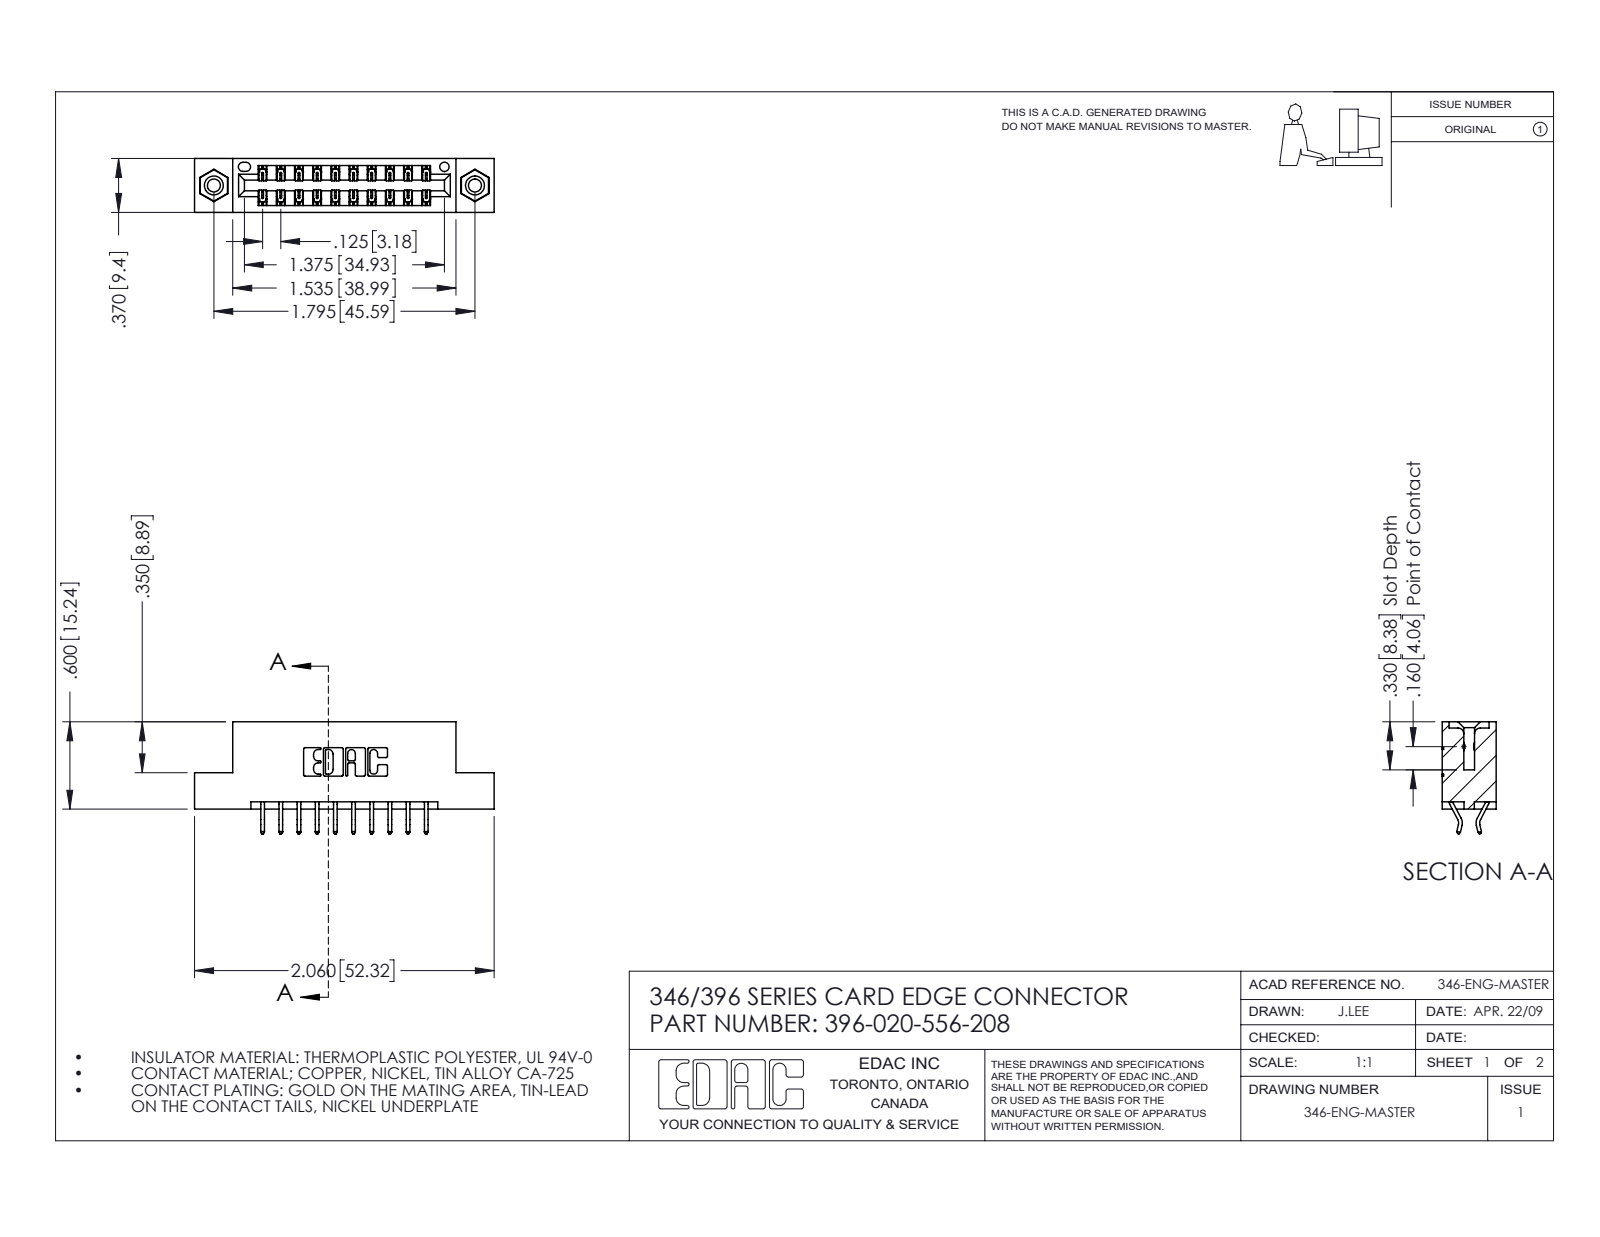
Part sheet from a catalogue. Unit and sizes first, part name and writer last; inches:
Units: inches
Overall size (bounding box): 2.06 × 0.77 × 0.37
Round holes (diameter × count): ⌀0.089 ×2, ⌀0.125 ×2, ⌀0.156 ×2, ⌀0.064 ×1
Round bosses / shafts (diameter × count): ⌀0.155 ×2
Partial cylindrical surfaces — rounded edges, fillets, slot ends (radius × count): R0.006 ×30, R0.01 ×22, R0.007 ×6, R0.031 ×6, R0.026 ×3, R0.01 ×2, R0.014 ×2, R0.022 ×2
Main face-to-face distances: 0.25, 0.048, 0.322, 0.37, 0.025, 0.072, 0.298, 0.148, 0.222, 0.1
Hole centre spacings: 0.246, 1.59, 1.795
Volume: 0.296 in³ · Surface area: 9.548 in²
Bodies: 23 solids, 1342 faces (888 planar, 438 cylindrical, 16 other)
Part name (STEP PRODUCT): 345-250-001_345-250-003-102; 396-020-556-208; 345-292-001_556 Tail; 346 Part_Flush Mounting Lugs - 0.156 Dia-TI
STEP written by: SolidWorks 2016 (CONFIG_CONTROL_DESIGN)
